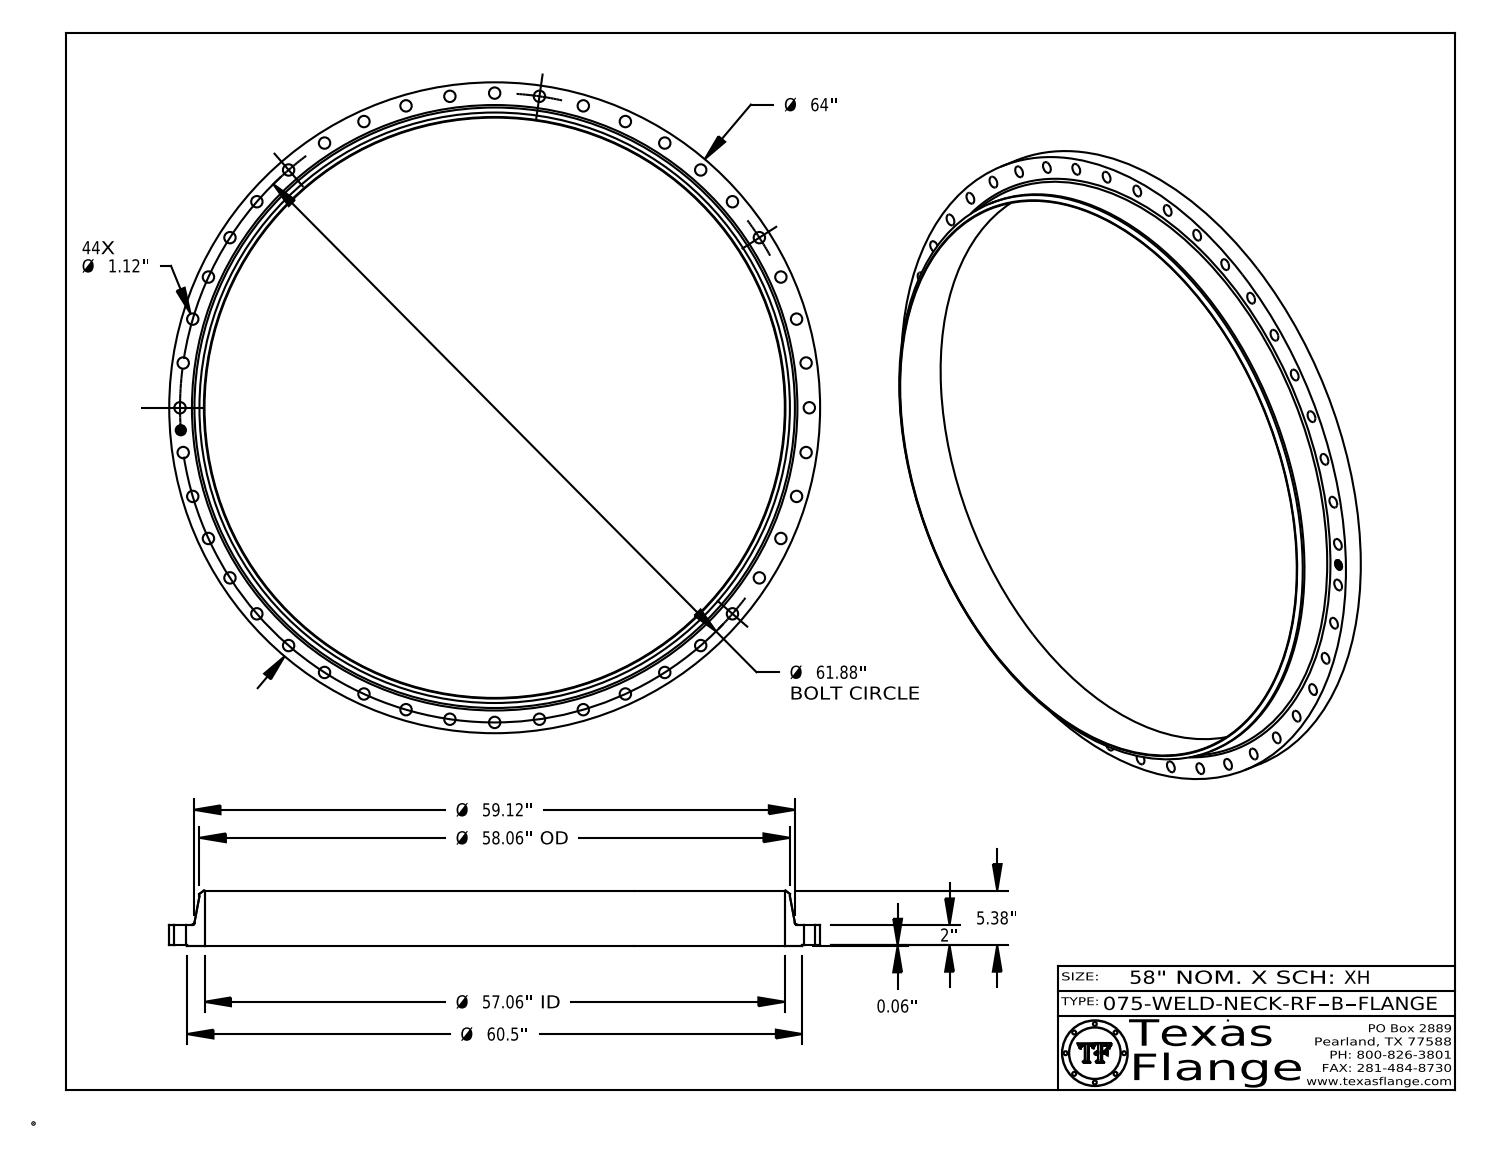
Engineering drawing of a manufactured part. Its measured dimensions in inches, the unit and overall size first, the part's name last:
Units: inches
Overall size (bounding box): 64 × 64 × 5.443
Round holes (diameter × count): ⌀1.12 ×44, ⌀1 ×1, ⌀57.06 ×1
Round bosses / shafts (diameter × count): ⌀0.061 ×8, ⌀64 ×1, ⌀60.5 ×1, ⌀58.06 ×1, ⌀0.788 ×1
Main face-to-face distances: 2.063, 0.063, 2, 5.443, 5.38, 3.38, 2.048, 1.985, 0.015, 3.395
Hole centre spacings: 61.722, 30.94, 61.25, 59.374, 8.806, 60.466, 17.434, 25.706
Volume: 1 683 in³ · Surface area: 3 412 in²
Bodies: 1 solid, 491 faces (369 planar, 116 cylindrical, 6 other)
Part name (STEP PRODUCT): 075-WELD-NECK-RF, Series B
STEP written by: CATIA V5 STEP AP214 (AUTOMOTIVE_DESIGN)
